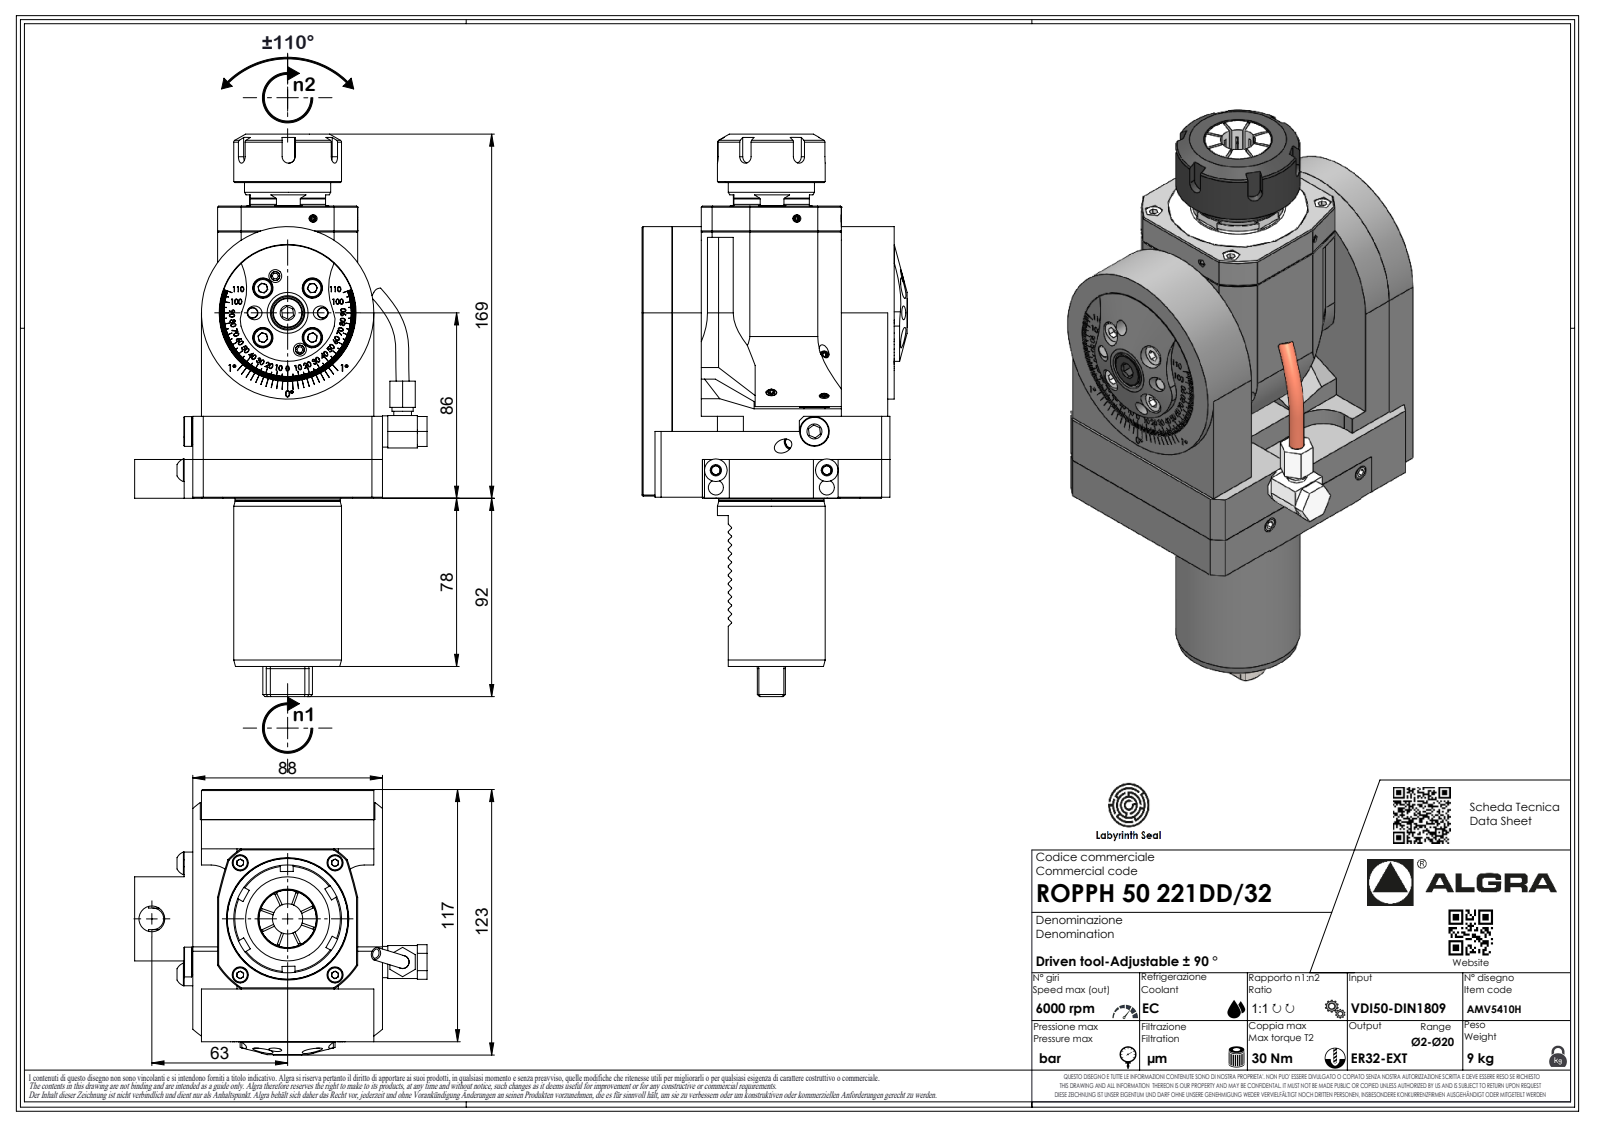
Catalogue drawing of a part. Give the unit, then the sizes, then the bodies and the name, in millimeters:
Units: millimetres
Overall size (bounding box): 260.91 × 135.7 × 123
Round holes (diameter × count): ⌀2.1 ×1
Round bosses / shafts (diameter × count): ⌀80 ×1, ⌀50 ×1, ⌀48.7 ×1, ⌀40 ×1, ⌀14.5 ×1, ⌀9.8 ×1, ⌀8.2 ×1, ⌀6.37 ×1
Partial cylindrical surfaces — rounded edges, fillets, slot ends (radius × count): R0.3 ×12, R3 ×11, R0.33 ×7, R0.52 ×7, R3.7 ×7, R10 ×2, R12 ×2, R28 ×2
Main face-to-face distances: 4, 84, 65, 0.5, 76.5, 11.5, 7.5, 24.5, 72.5, 27.5
Volume: 1 272 000 mm³ · Surface area: 110 551 mm²
Bodies: 1 solid, 640 faces (411 planar, 98 cylindrical, 131 other)
Part name (STEP PRODUCT): ROPPH50221DD32
STEP written by: SolidWorks 2023 (AUTOMOTIVE_DESIGN)
